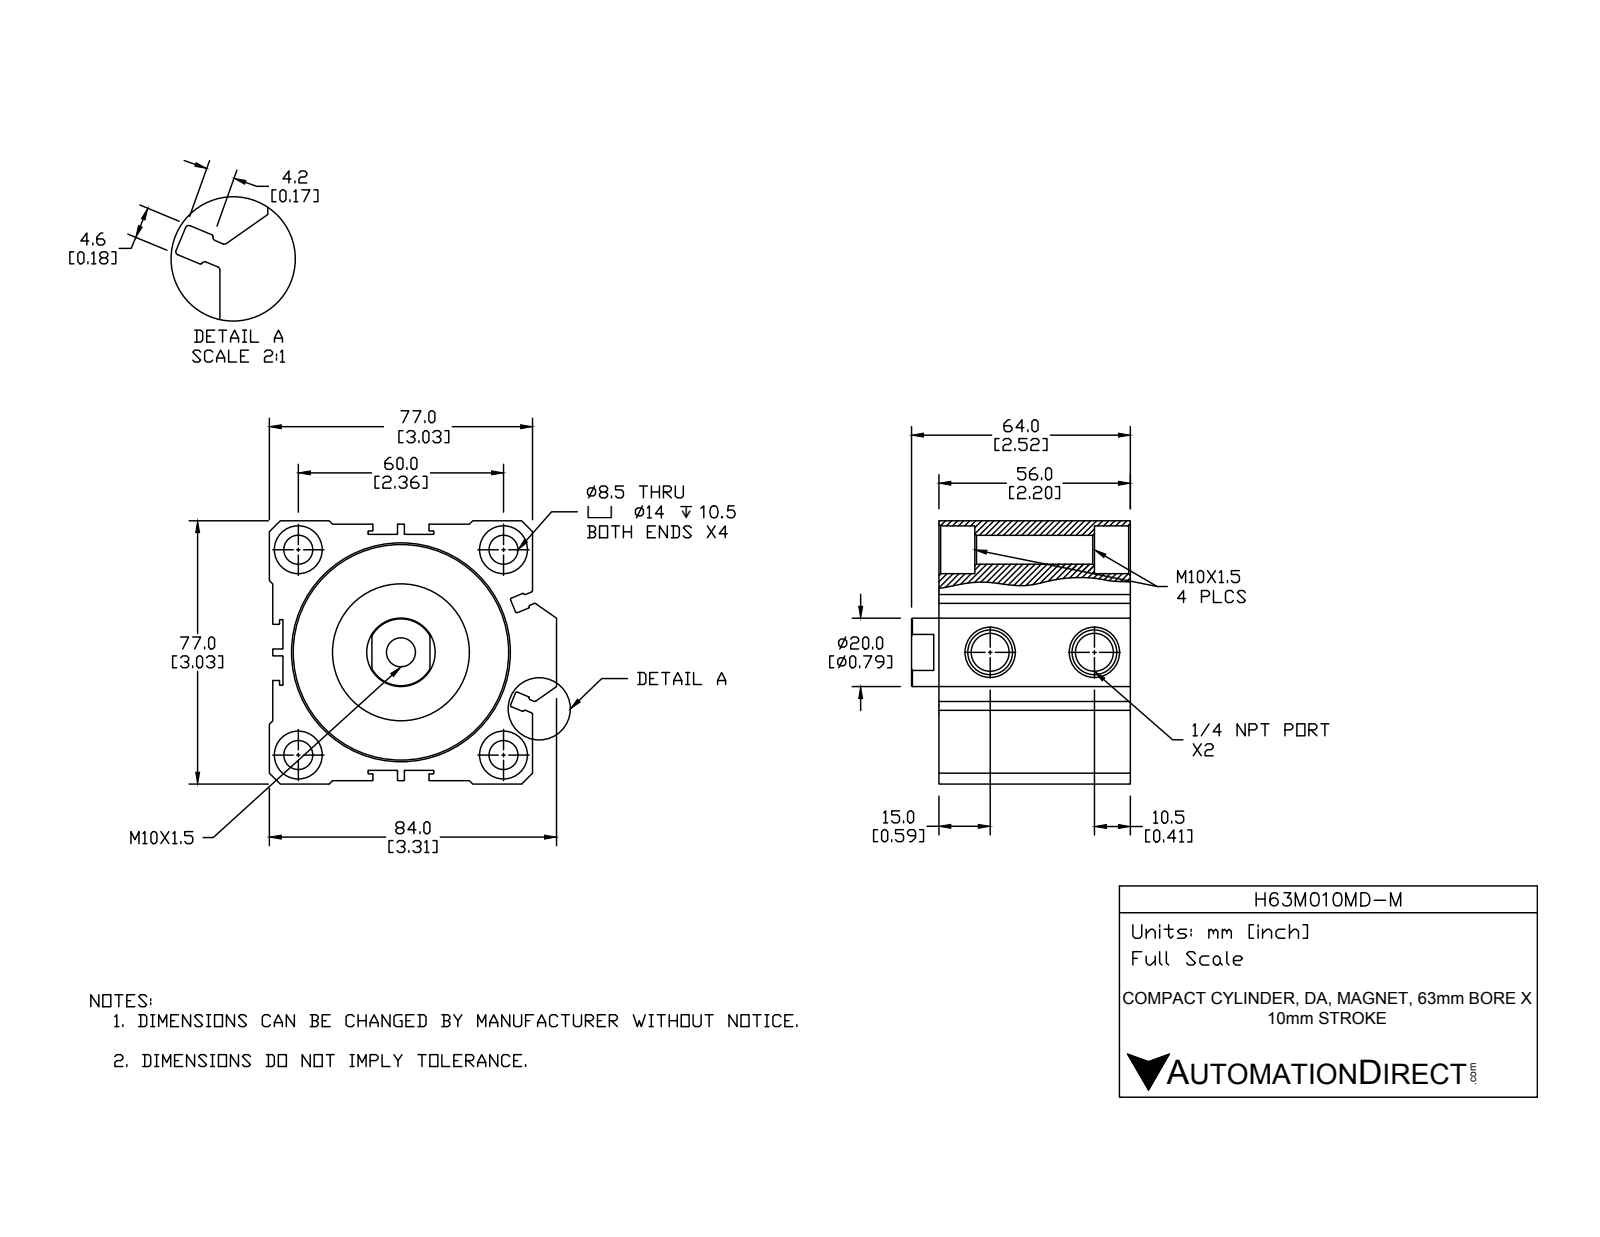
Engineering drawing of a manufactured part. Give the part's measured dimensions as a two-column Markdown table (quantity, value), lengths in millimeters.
| quantity | value |
| --- | --- |
| part name | H63M010MD-M; H63M010MD-M-BODY; H63M010MD-M-PISTON |
| STEP written by | SolidWorks 2015 (CONFIG_CONTROL_DESIGN) |
| units | millimeters |
| bodies | 2 solids, 255 faces (99 planar, 103 cylindrical, 53 other) |
| overall size | 84 × 77 × 64 |
| volume | 253 771 mm³ |
| surface area | 69 658 mm² |
| round holes (diameter × count) | 8.5 × 5, 14 × 4, 11.13 × 2, 20 × 1, 45.51 × 1, 63 × 1 |
| round bosses / shafts (diameter × count) | 40 × 1, 39 × 1 |
| partial cylindrical surfaces (radius × count) | 0.2 × 40, 0.5 × 12 |
| main face-to-face distances | 1, 76, 33.5, 10.5, 3, 77, 4, 23, 73, 2 |
| hole center spacings | 42.43, 60, 84.85, 30.5 |
